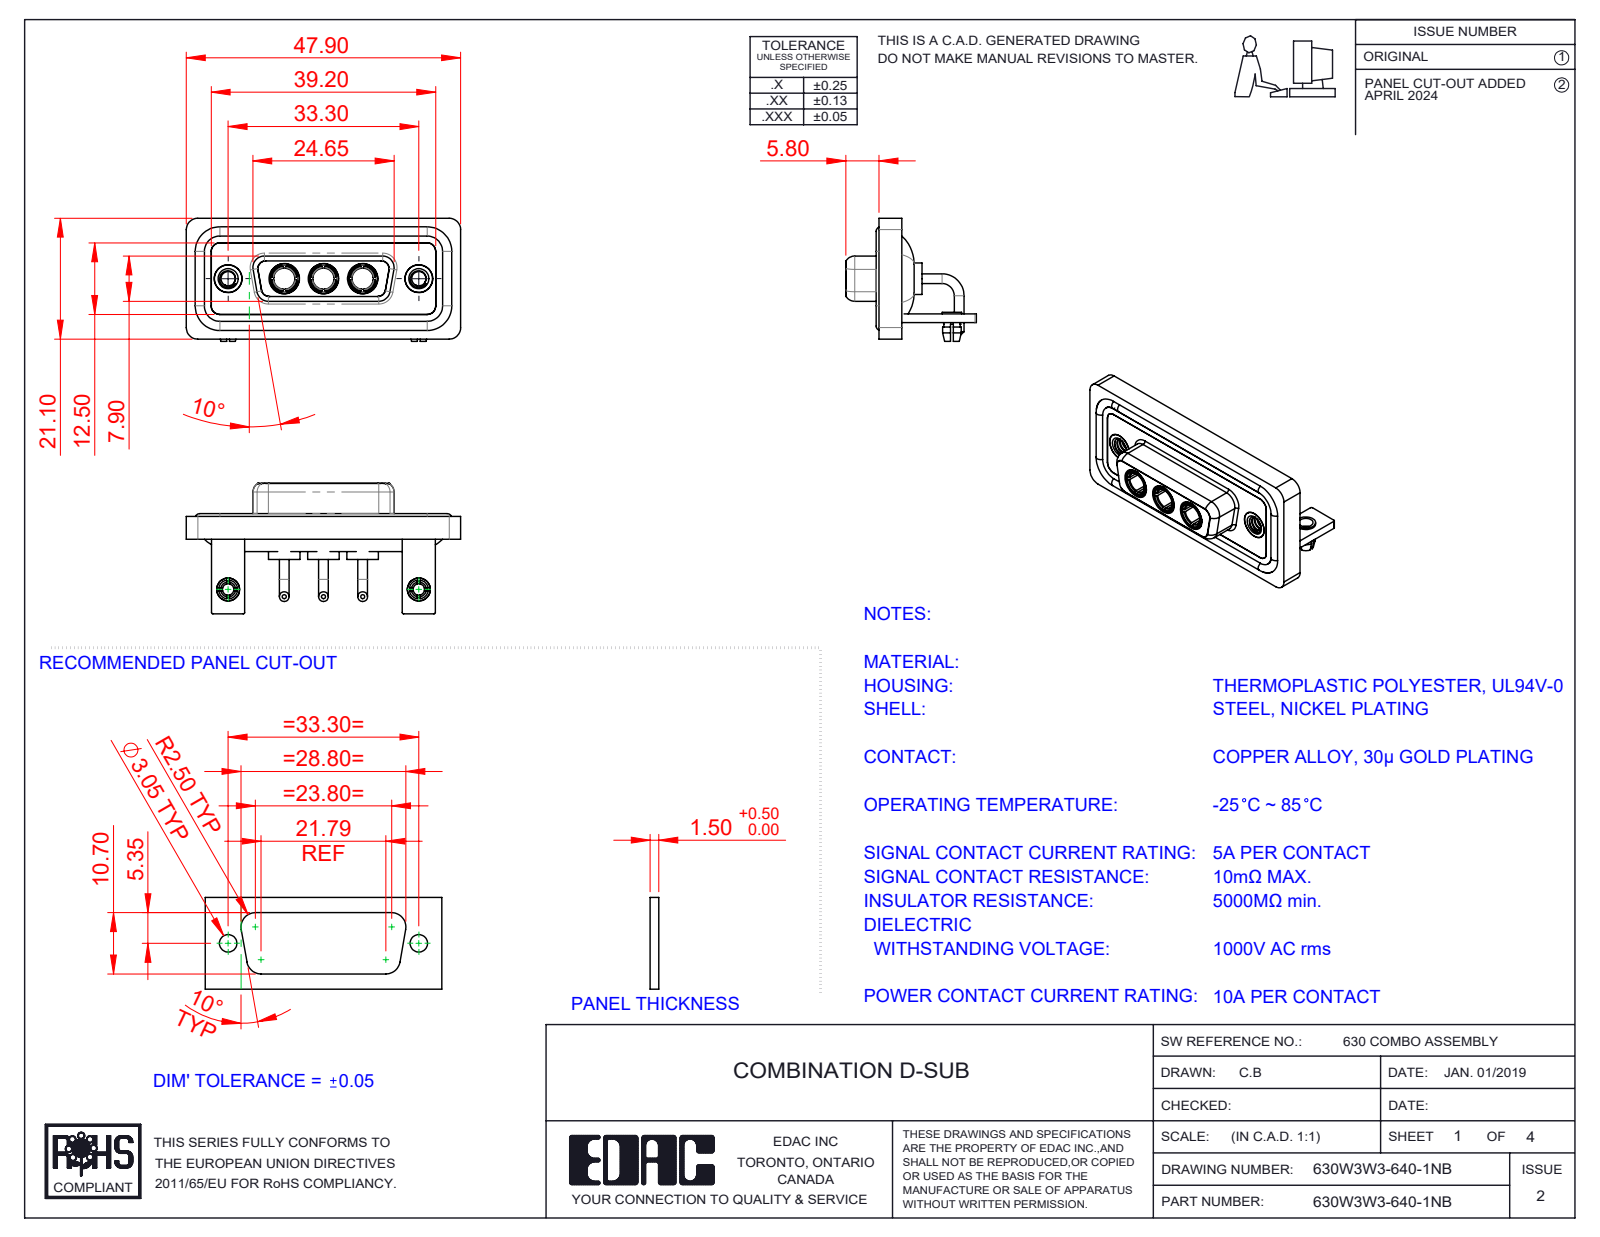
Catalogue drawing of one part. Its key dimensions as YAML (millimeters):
part_name: "630Combo Housing_3W3; 630Combo Shell Front_15 Contacts; Power Socket_10A RA; 630Combo Shell Rear_15 Contacts (+5 more)"
step_written_by: "SolidWorks 2023 (CONFIG_CONTROL_DESIGN)"
units: millimeters
bodies: {solids: 17, faces: 754, planar: 260, cylindrical: 317, other: 177}
overall_size: [47.9, 22.8, 21.5]
volume: 6402
surface_area: 10769
round_holes:
  - {diameter: 4.85, count: 5}
  - {diameter: 2.5, count: 4}
  - {diameter: 3.7, count: 3}
  - {diameter: 5.3, count: 3}
  - {diameter: 2, count: 2}
  - {diameter: 3.2, count: 2}
  - {diameter: 4, count: 2}
  - {diameter: 4.05, count: 2}
  - {diameter: 5, count: 2}
round_bosses_or_shafts:
  - {diameter: 1.7, count: 6}
  - {diameter: 1.6, count: 4}
  - {diameter: 5.5, count: 3}
  - {diameter: 5.2, count: 3}
  - {diameter: 4.96, count: 3}
  - {diameter: 4.75, count: 3}
  - {diameter: 3.75, count: 3}
  - {diameter: 4.95, count: 2}
partial_cylinders:
  - {radius: 2, count: 21}
  - {radius: 1.5, count: 18}
  - {radius: 0.25, count: 16}
  - {radius: 1.35, count: 12}
  - {radius: 1.6, count: 8}
  - {radius: 0.5, count: 5}
  - {radius: 0.6, count: 4}
  - {radius: 0.65, count: 4}
face_to_face_distances: [0.4, 2.9, 1.5, 1.8, 3.7, 1.1, 4.1, 1.6, 2.5, 1.4]
hole_center_spacings: [6.85, 9.8, 16.65, 23.5, 33.3, 13.7]
